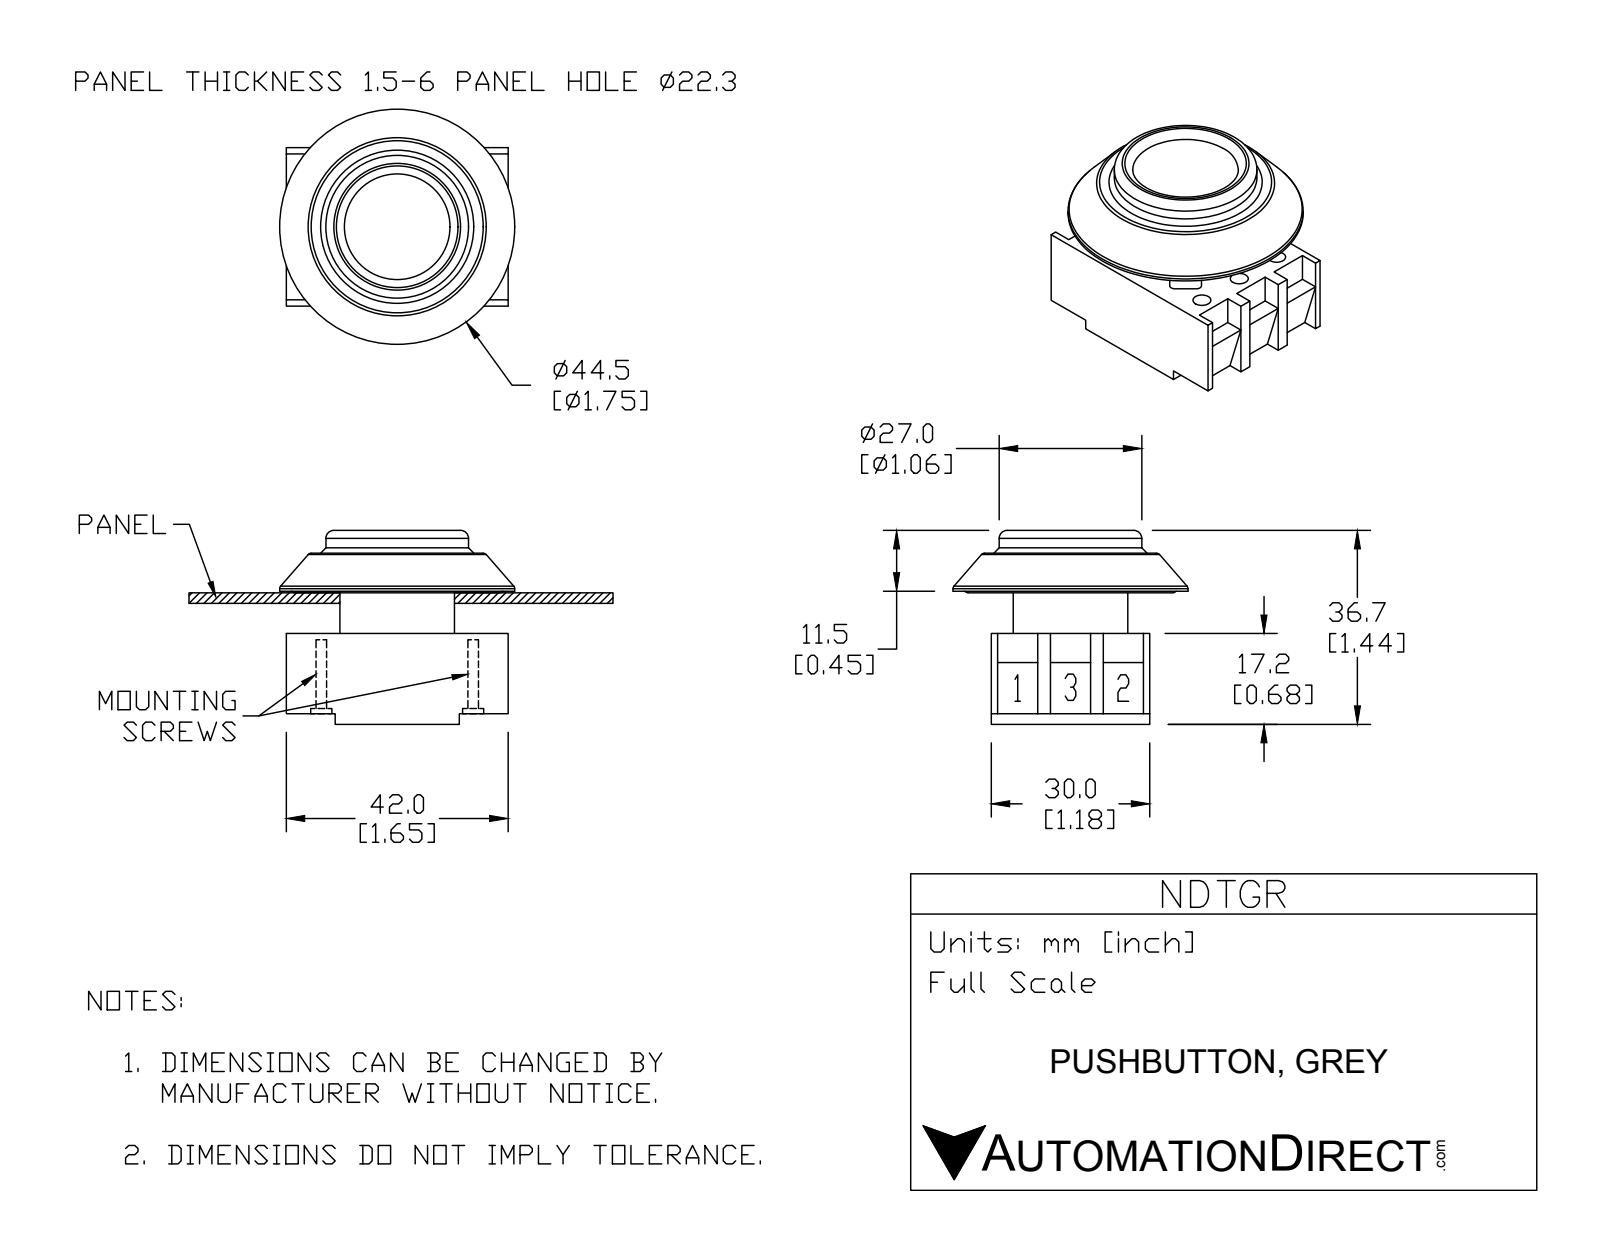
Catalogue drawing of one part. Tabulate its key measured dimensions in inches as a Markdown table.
| quantity | value |
| --- | --- |
| part name | NDTGR |
| STEP written by | SolidWorks 2015 (AUTOMOTIVE_DESIGN) |
| units | inches |
| bodies | 7 solids, 217 faces (127 planar, 65 cylindrical, 25 other) |
| overall size | 1.752 × 1.752 × 1.445 |
| volume | 1.533 in³ |
| surface area | 25.91 in² |
| round holes (diameter × count) | 0.134 × 6, 0.197 × 6, 0.492 × 1 |
| round bosses / shafts (diameter × count) | 0.181 × 2, 0.157 × 2, 1.752 × 1, 1.063 × 1, 0.854 × 1 |
| partial cylindrical surfaces (radius × count) | 0.039 × 8, 0.343 × 5, 0.433 × 1 |
| main face-to-face distances | 0.283, 0.598, 1.181, 0.394, 0.315, 0.295, 0.303, 0.406, 0.709, 0.913 |
| hole center spacings | 0.394, 0.69, 1.199, 1.132, 0.566, 0.787, 1.379 |
